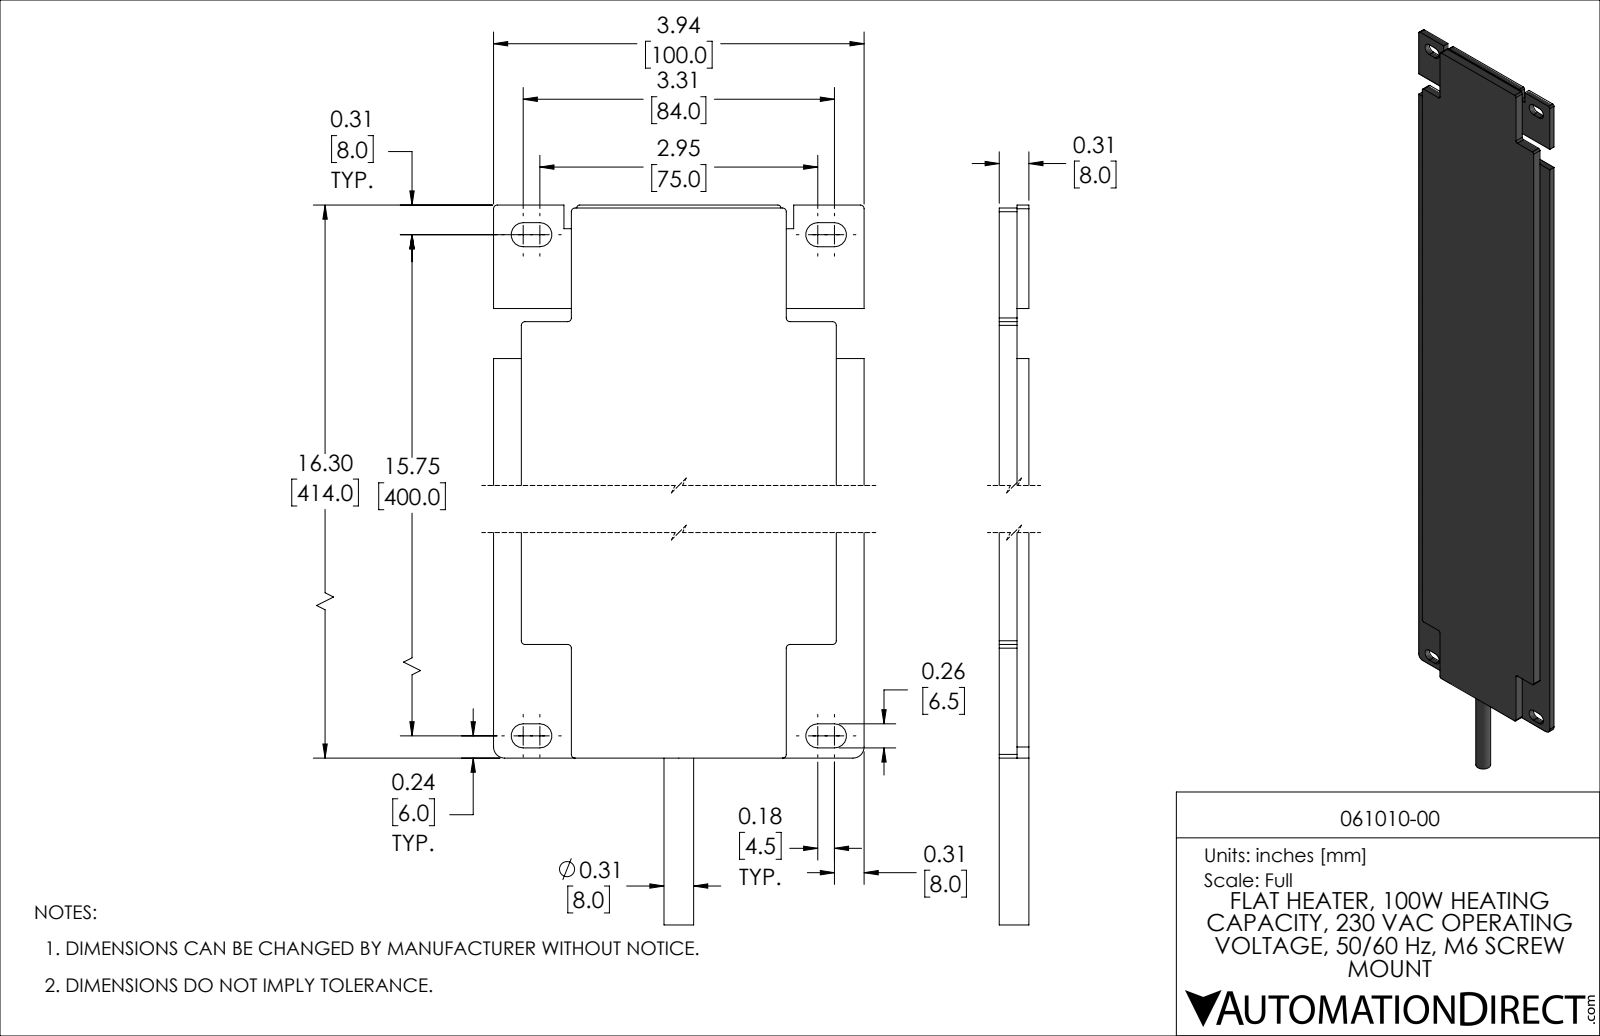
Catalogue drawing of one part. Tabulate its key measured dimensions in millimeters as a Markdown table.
| quantity | value |
| --- | --- |
| part name | PRODUCT_NAME_1 |
| STEP written by | ACIS (AUTOMOTIVE_DESIGN_CC2) |
| units | millimeters |
| bodies | 1 solid, 76 faces (48 planar, 28 cylindrical, 0 other) |
| overall size | 459 × 100 × 8 |
| volume | 290 107 mm³ |
| surface area | 91 816 mm² |
| round bosses / shafts (diameter × count) | 8 × 1 |
| partial cylindrical surfaces (radius × count) | 1 × 14, 3.25 × 8, 0.8 × 2, 3 × 2 |
| main face-to-face distances | 8, 4.8, 3.2, 7.5, 92.5, 85, 100, 21, 79, 13.5 |
